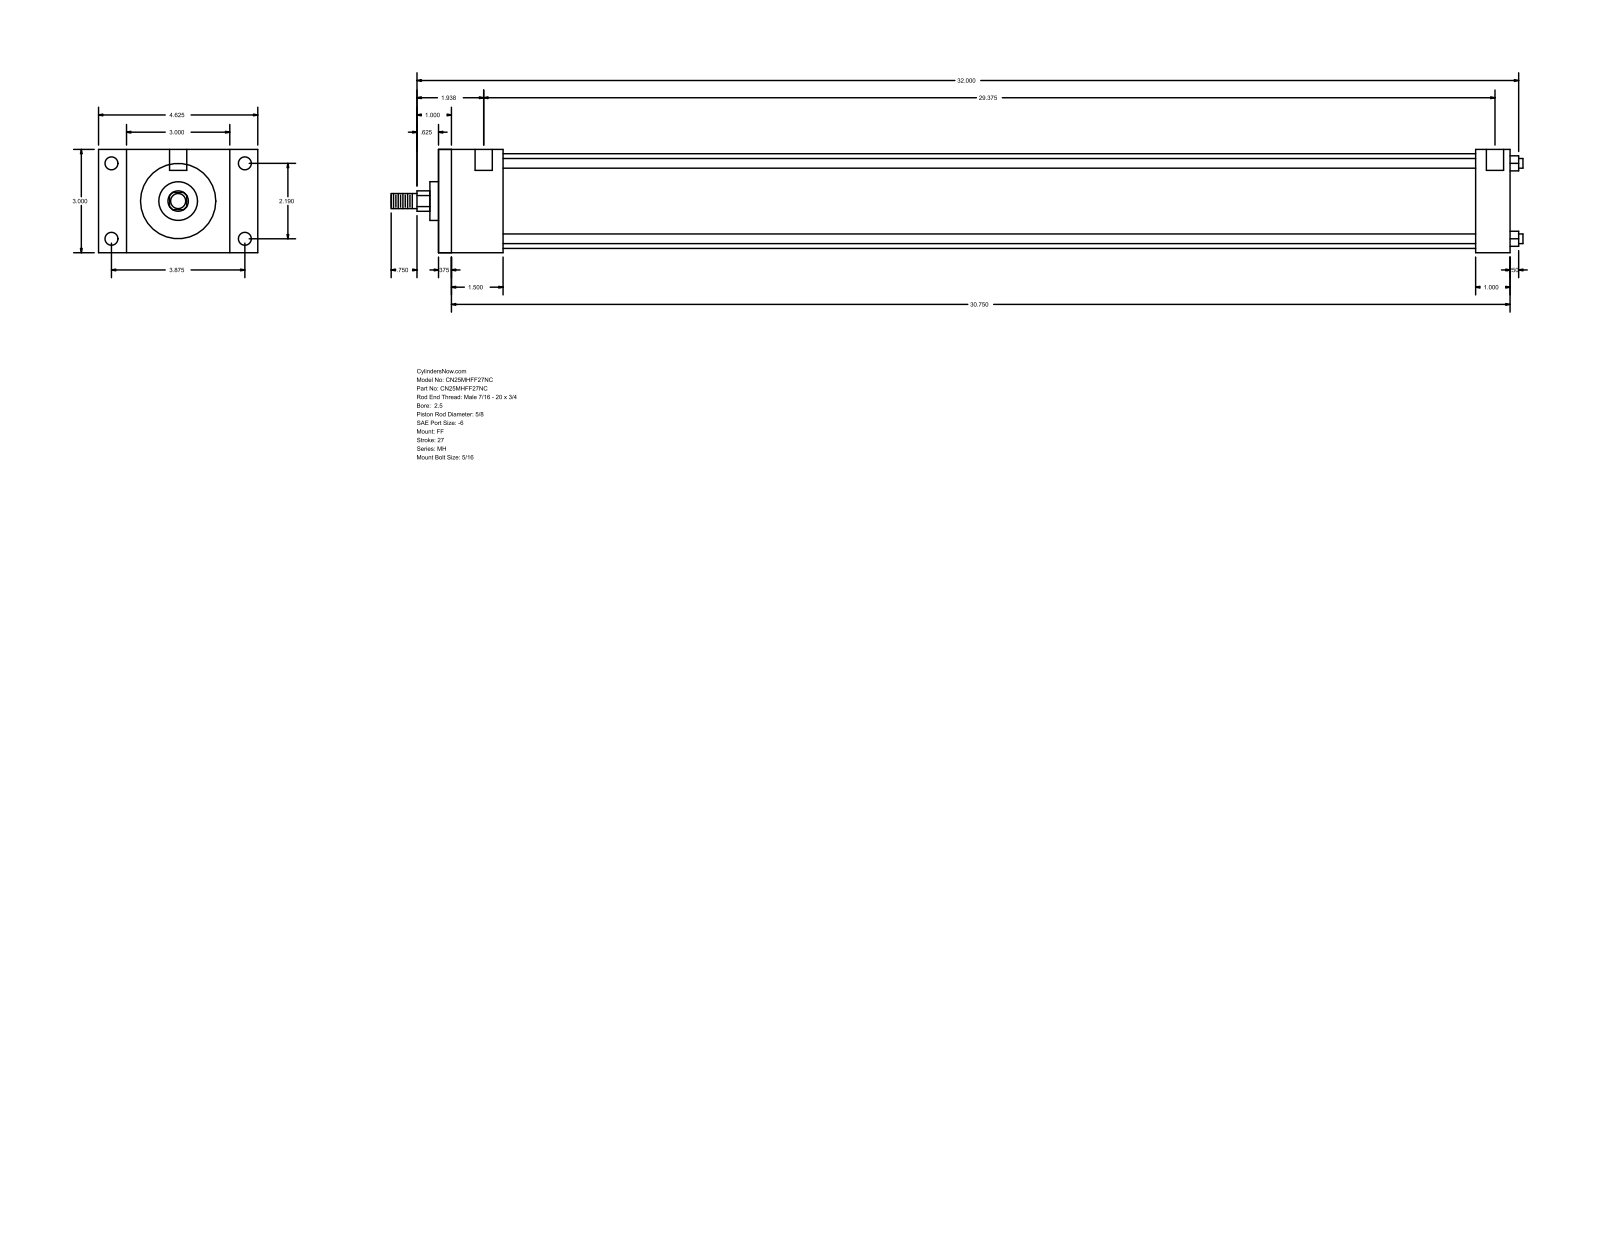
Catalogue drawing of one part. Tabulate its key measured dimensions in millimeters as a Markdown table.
| quantity | value |
| --- | --- |
| part name | MH_FF__0250_0.625 |
| STEP written by | GSSL Pune (CONFIG_CONTROL_DESIGN) |
| units | millimeters |
| bodies | 0 solids, 92 faces (64 planar, 28 cylindrical, 0 other) |
| overall size | 835.02 × 117.47 × 76.2 |
| round holes (diameter × count) | 5.56 × 4, 9.53 × 4, 12.7 × 2 |
| round bosses / shafts (diameter × count) | 7.14 × 4, 69.85 × 1, 28.57 × 1, 15.88 × 1, 11.11 × 1 |
| partial cylindrical surfaces (radius × count) | 7.54 × 1 |
| main face-to-face distances | 76.2, 790.57, 781.05, 9.52, 25.4, 47.62, 765.17, 38.1, 755.65, 717.55 |
| hole center spacings | 55.62, 98.42, 113.05, 754.06, 3.17, 4.76, 746.13, 749.3 |
